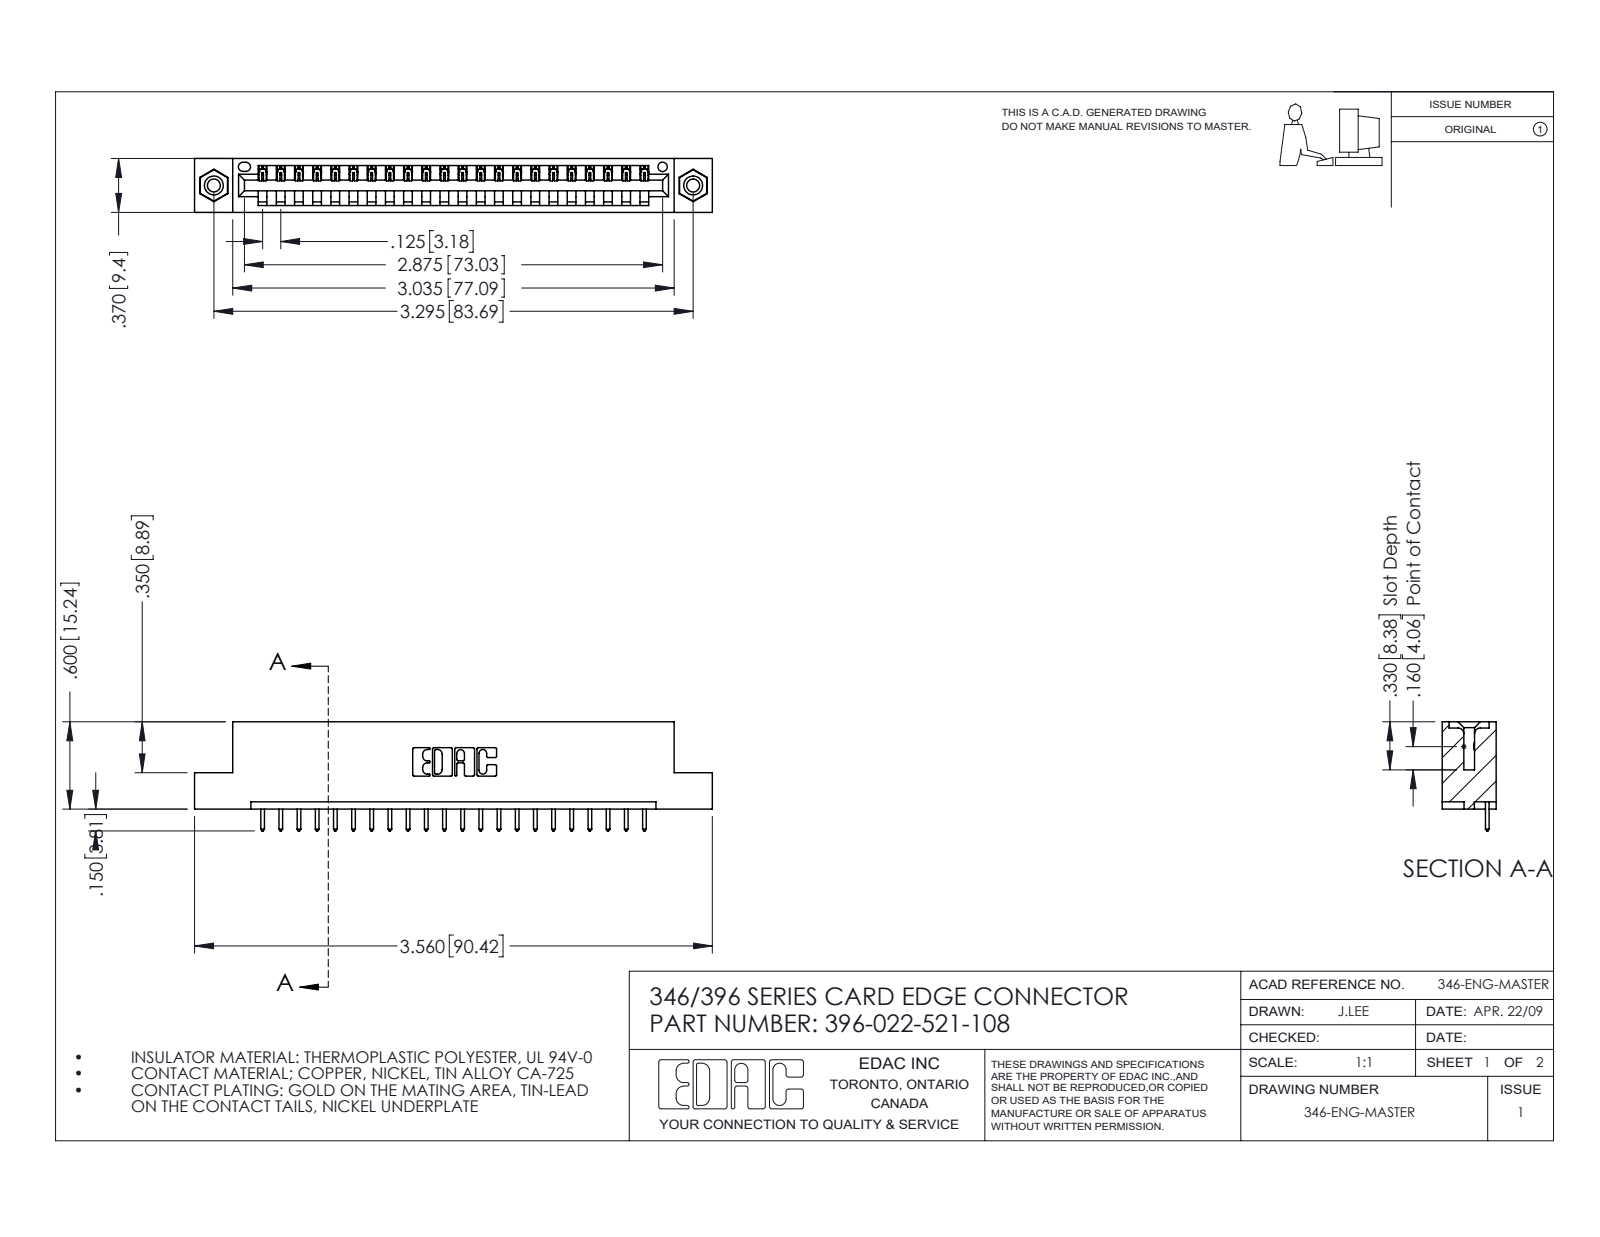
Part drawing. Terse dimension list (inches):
name: 396-022-521-108; 345-250-001_345-250-003-102; 345-292-001_345-293-121; 346 Part_Flush Mounting Lugs - 0.156 Dia-TI
written by: SolidWorks 2016 (CONFIG_CONTROL_DESIGN)
unit: in
bodies: 25 solids, 1458 faces (988 planar, 454 cylindrical, 16 other)
size: 3.56 × 0.75 × 0.37
volume: 0.516 in³; area: 15.68 in²
holes: 2× ⌀0.089, 2× ⌀0.125, 2× ⌀0.156, 1× ⌀0.064
bosses: 2× ⌀0.155
rounds: 44× R0.006, 44× R0.01, 22× R0.01, 6× R0.007, 6× R0.031, 3× R0.026, 2× R0.031, 2× R0.04
face distances: 0.048, 0.322, 0.37, 0.25, 0.072, 0.298, 0.025, 0.148, 0.222, 0.1
hole spacings: 0.246, 3.087, 3.295
